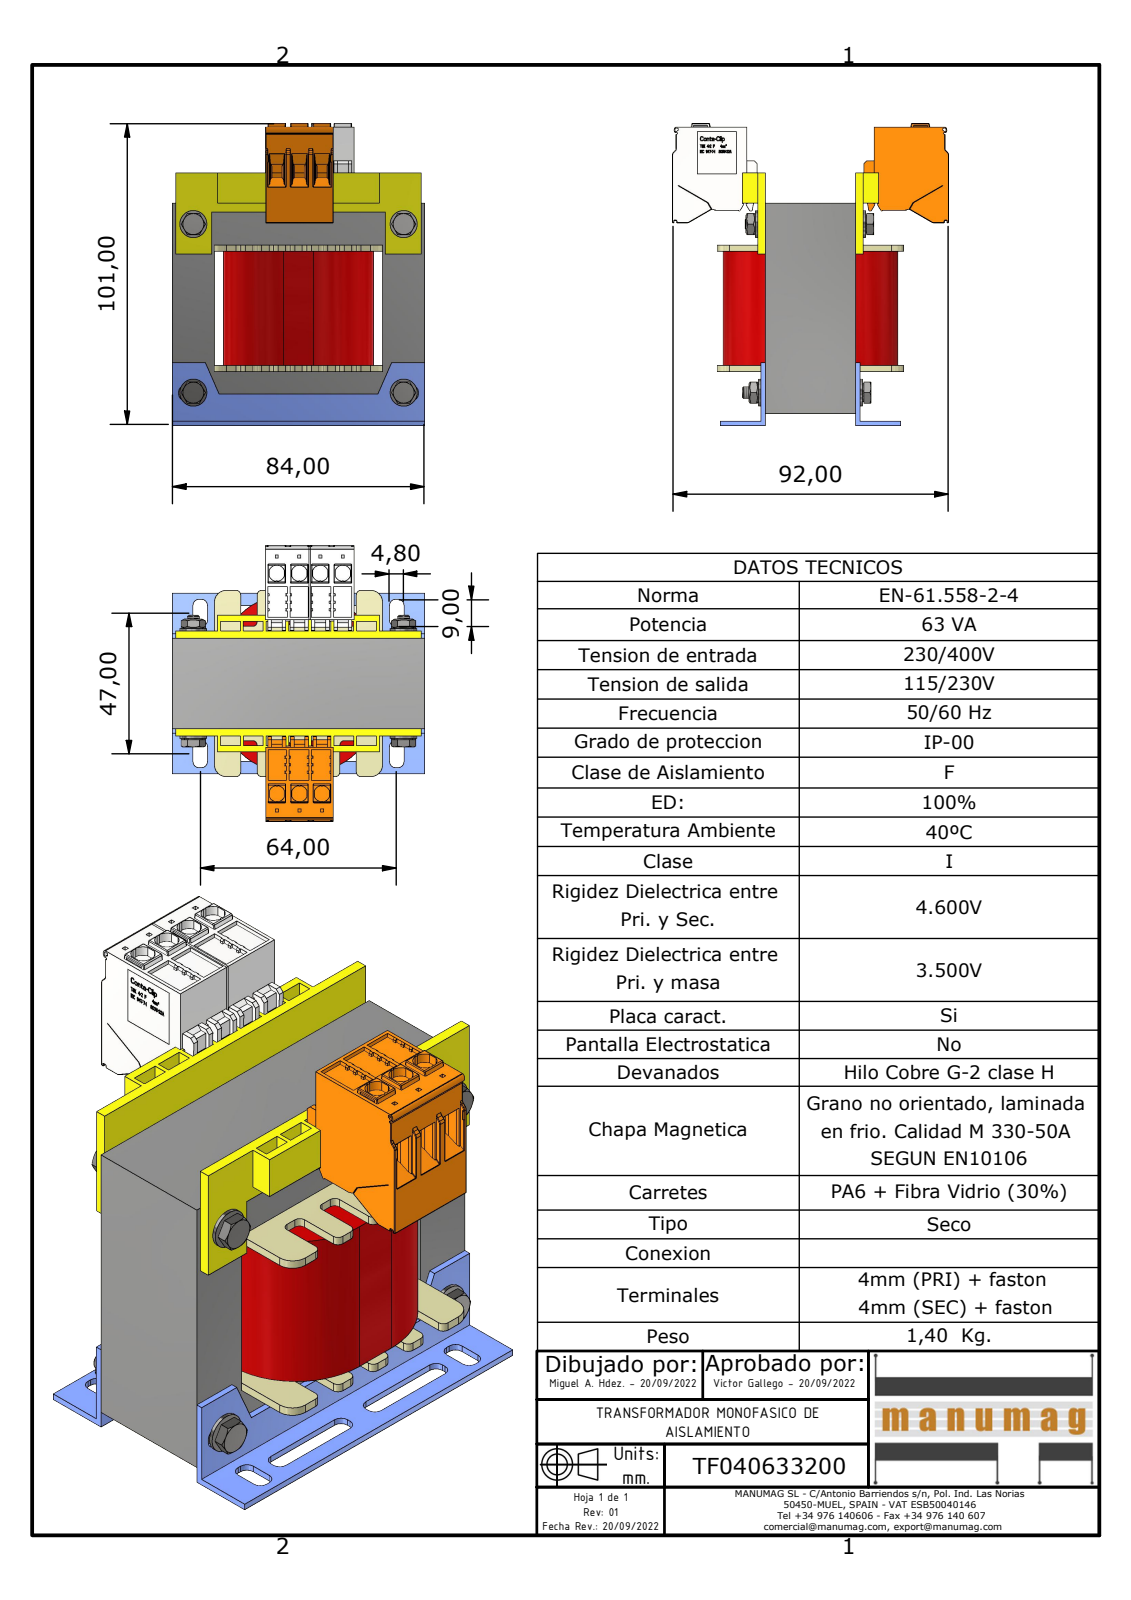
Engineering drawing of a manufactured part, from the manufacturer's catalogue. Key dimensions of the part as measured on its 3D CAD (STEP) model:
Part name (STEP PRODUCT): TF040633200; EI84 x 70 - 30 (RC28); EI 84 X 70 - 30; AF28DIN (+6 more)
STEP written by: Autodesk Inventor 2023 (AUTOMOTIVE_DESIGN)
Units: millimetres
Bodies: 25 solids, 5812 faces (4692 planar, 757 cylindrical, 363 other)
Overall size (bounding box): 100.5 × 91.9 × 84
Volume: 259 753 mm³ · Surface area: 91 404 mm²
Round holes (diameter × count): ⌀3.24 ×4, ⌀4.3 ×4, ⌀4.5 ×4, ⌀4 ×2
Round bosses / shafts (diameter × count): ⌀9 ×4, ⌀5.9 ×4, ⌀3.62 ×4, ⌀4 ×2
Partial cylindrical surfaces — rounded edges, fillets, slot ends (radius × count): R0.15 ×271, R0.2 ×86, R2 ×40, R1.5 ×32, R0.5 ×22, R0.3 ×12, R1 ×8, R2.7 ×7
Main face-to-face distances: 14, 56, 30, 28, 42, 70, 2.5, 1.5, 2, 84
Hole centre spacings: 56, 70, 89.64
